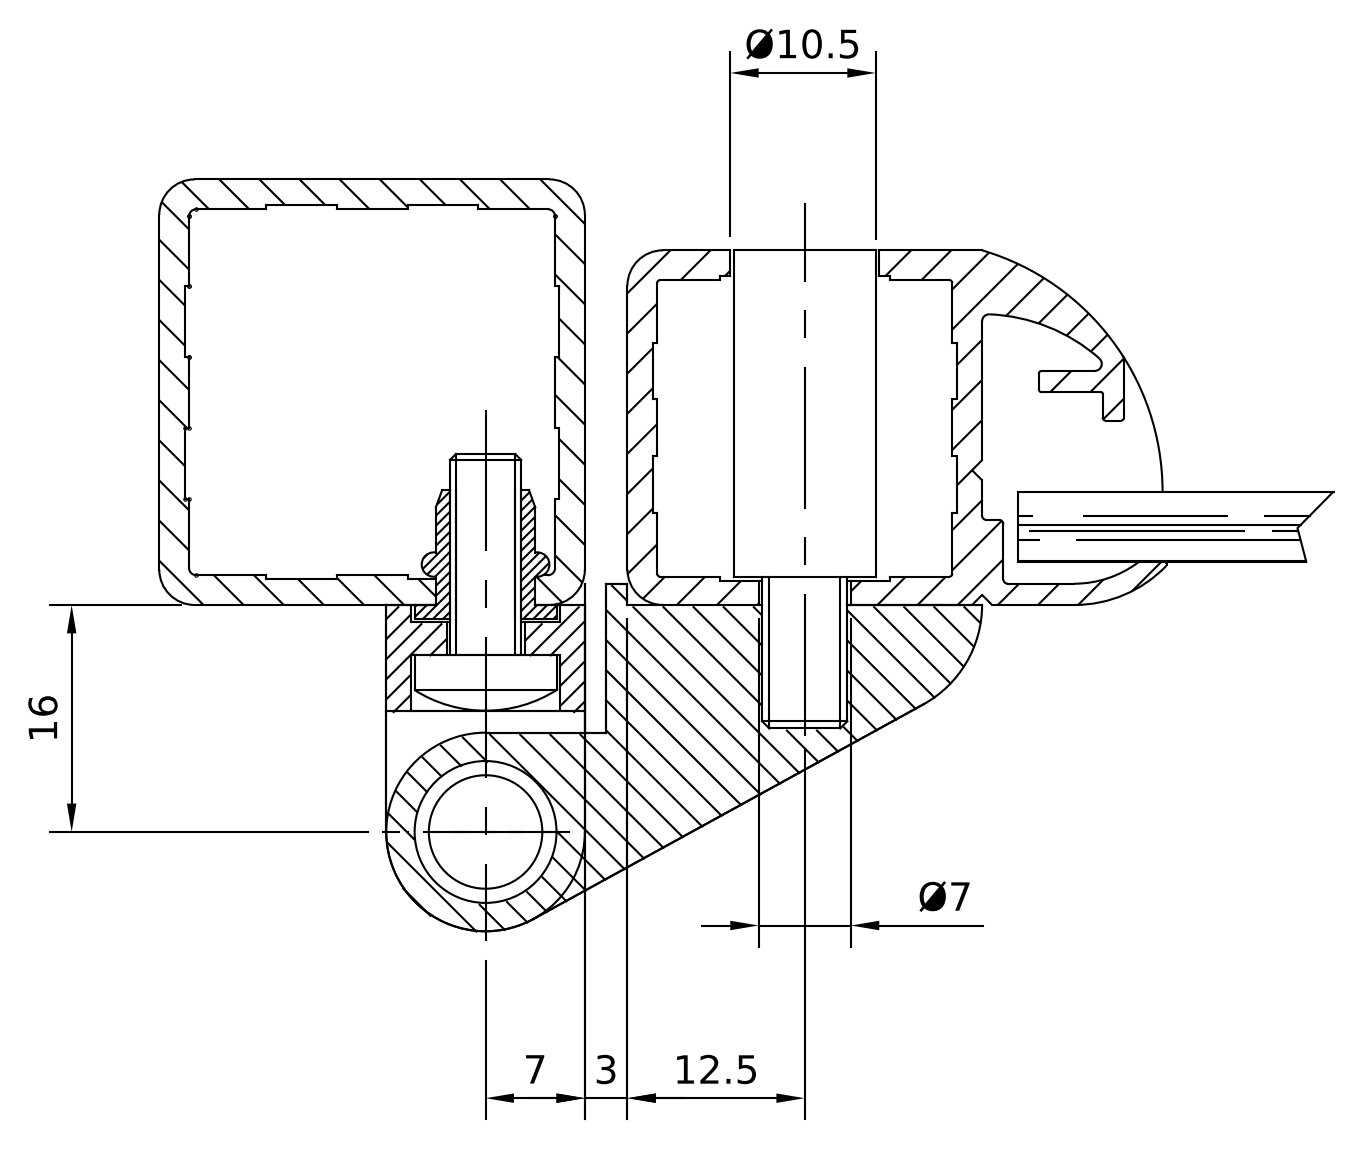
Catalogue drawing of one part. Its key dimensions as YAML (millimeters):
step_written_by: "THINKDESIGN (CONFIG_CONTROL_DESIGN)"
units: millimeters
bodies: {solids: 6, faces: 67, planar: 38, cylindrical: 25, other: 4}
overall_size: [66.5, 58, 42]
volume: 27559
surface_area: 15199
round_holes:
  - {diameter: 5.5, count: 2}
  - {diameter: 10.5, count: 2}
  - {diameter: 5, count: 1}
  - {diameter: 8, count: 1}
round_bosses_or_shafts:
  - {diameter: 10, count: 2}
  - {diameter: 14, count: 1}
  - {diameter: 6, count: 1}
partial_cylinders:
  - {radius: 14.26, count: 1}
face_to_face_distances: [1.5, 10, 45, 14, 46.5, 35, 55, 9, 15.5, 7.5]
hole_center_spacings: [25.74, 25]
